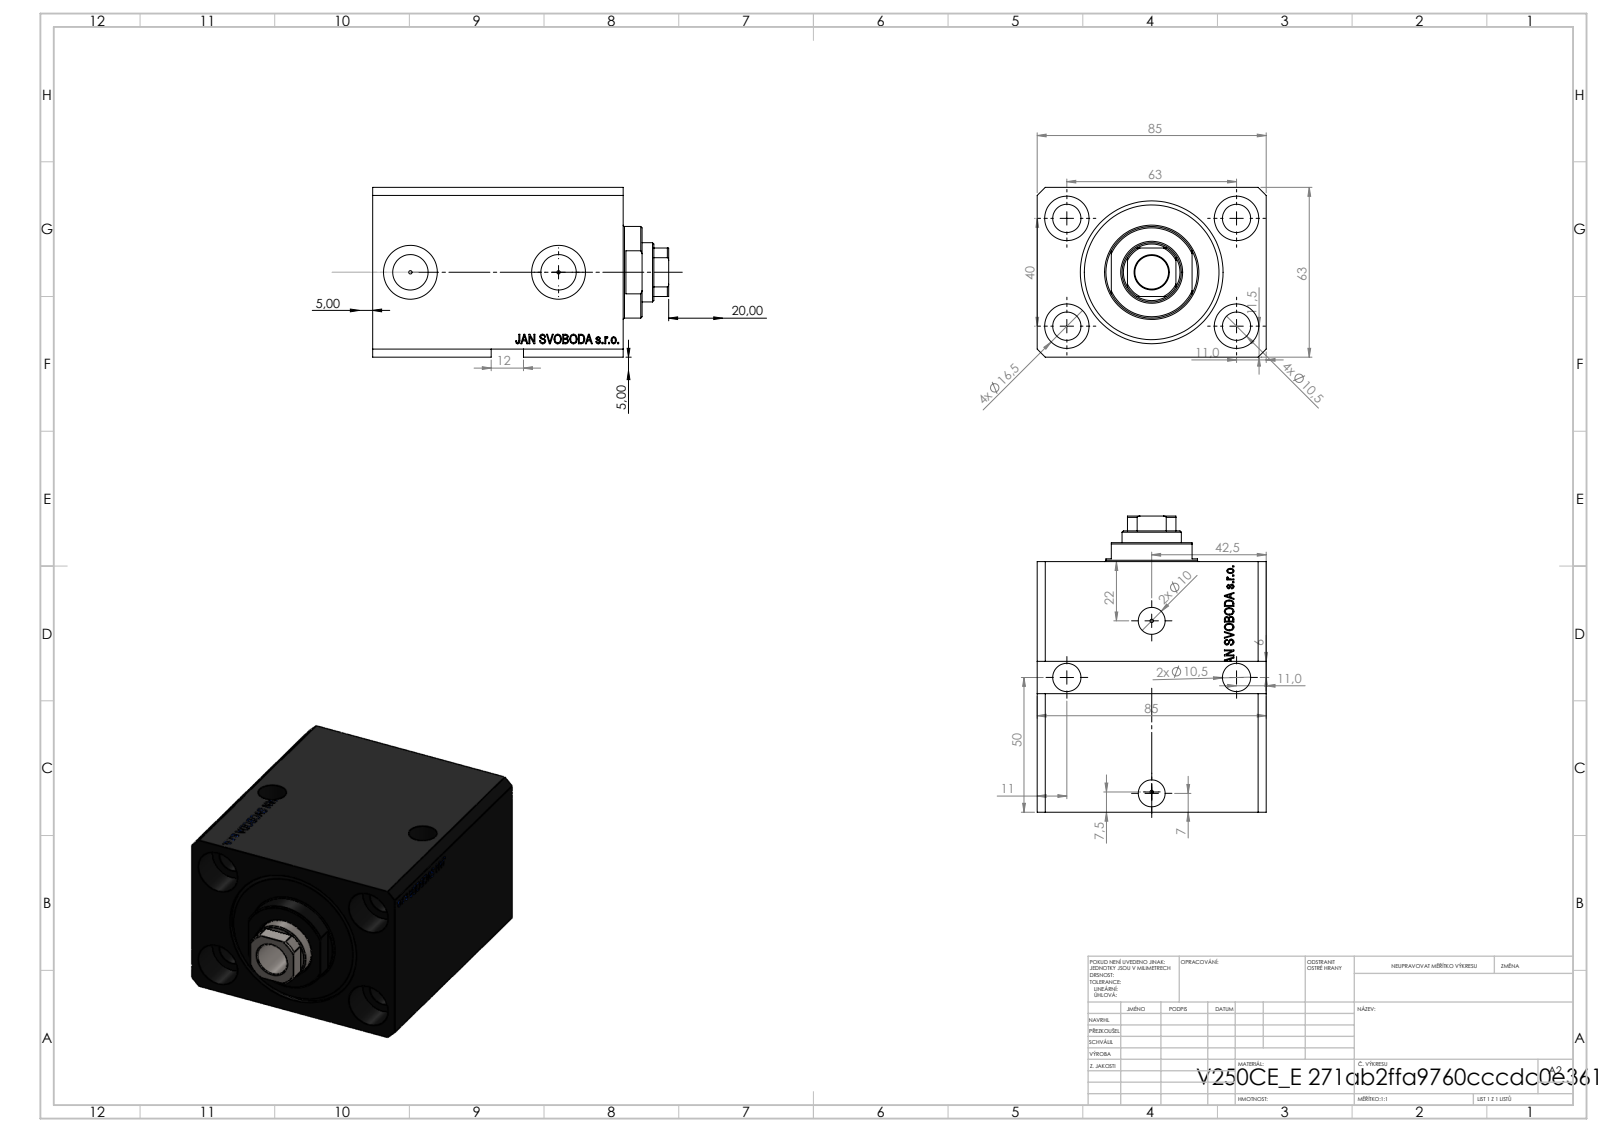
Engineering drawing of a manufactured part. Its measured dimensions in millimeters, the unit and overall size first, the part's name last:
Units: millimetres
Overall size (bounding box): 109.9 × 85 × 63
Round holes (diameter × count): ⌀10.5 ×6, ⌀1.25 ×4, ⌀16.5 ×4, ⌀10 ×2, ⌀13.16 ×2, ⌀20 ×2, ⌀12.5 ×1, ⌀22 ×1, ⌀40 ×1, ⌀53 ×1
Round bosses / shafts (diameter × count): ⌀34 ×1
Partial cylindrical surfaces — rounded edges, fillets, slot ends (radius × count): R10.5 ×1
Main face-to-face distances: 63, 85, 93, 65.9, 27.1, 11.4, 54.5, 81.6, 11, 82
Hole centre spacings: 37.31, 63, 37.86, 40, 52.88, 53.3, 74.63, 0.53
Volume: 427 151 mm³ · Surface area: 89 410 mm²
Bodies: 3 solids, 917 faces (459 planar, 84 cylindrical, 374 other)
Part name (STEP PRODUCT): V250CE_E_Body; V250CE_C_VCP; V250CE_VC_E
STEP written by: SolidWorks 2019 (CONFIG_CONTROL_DESIGN)
